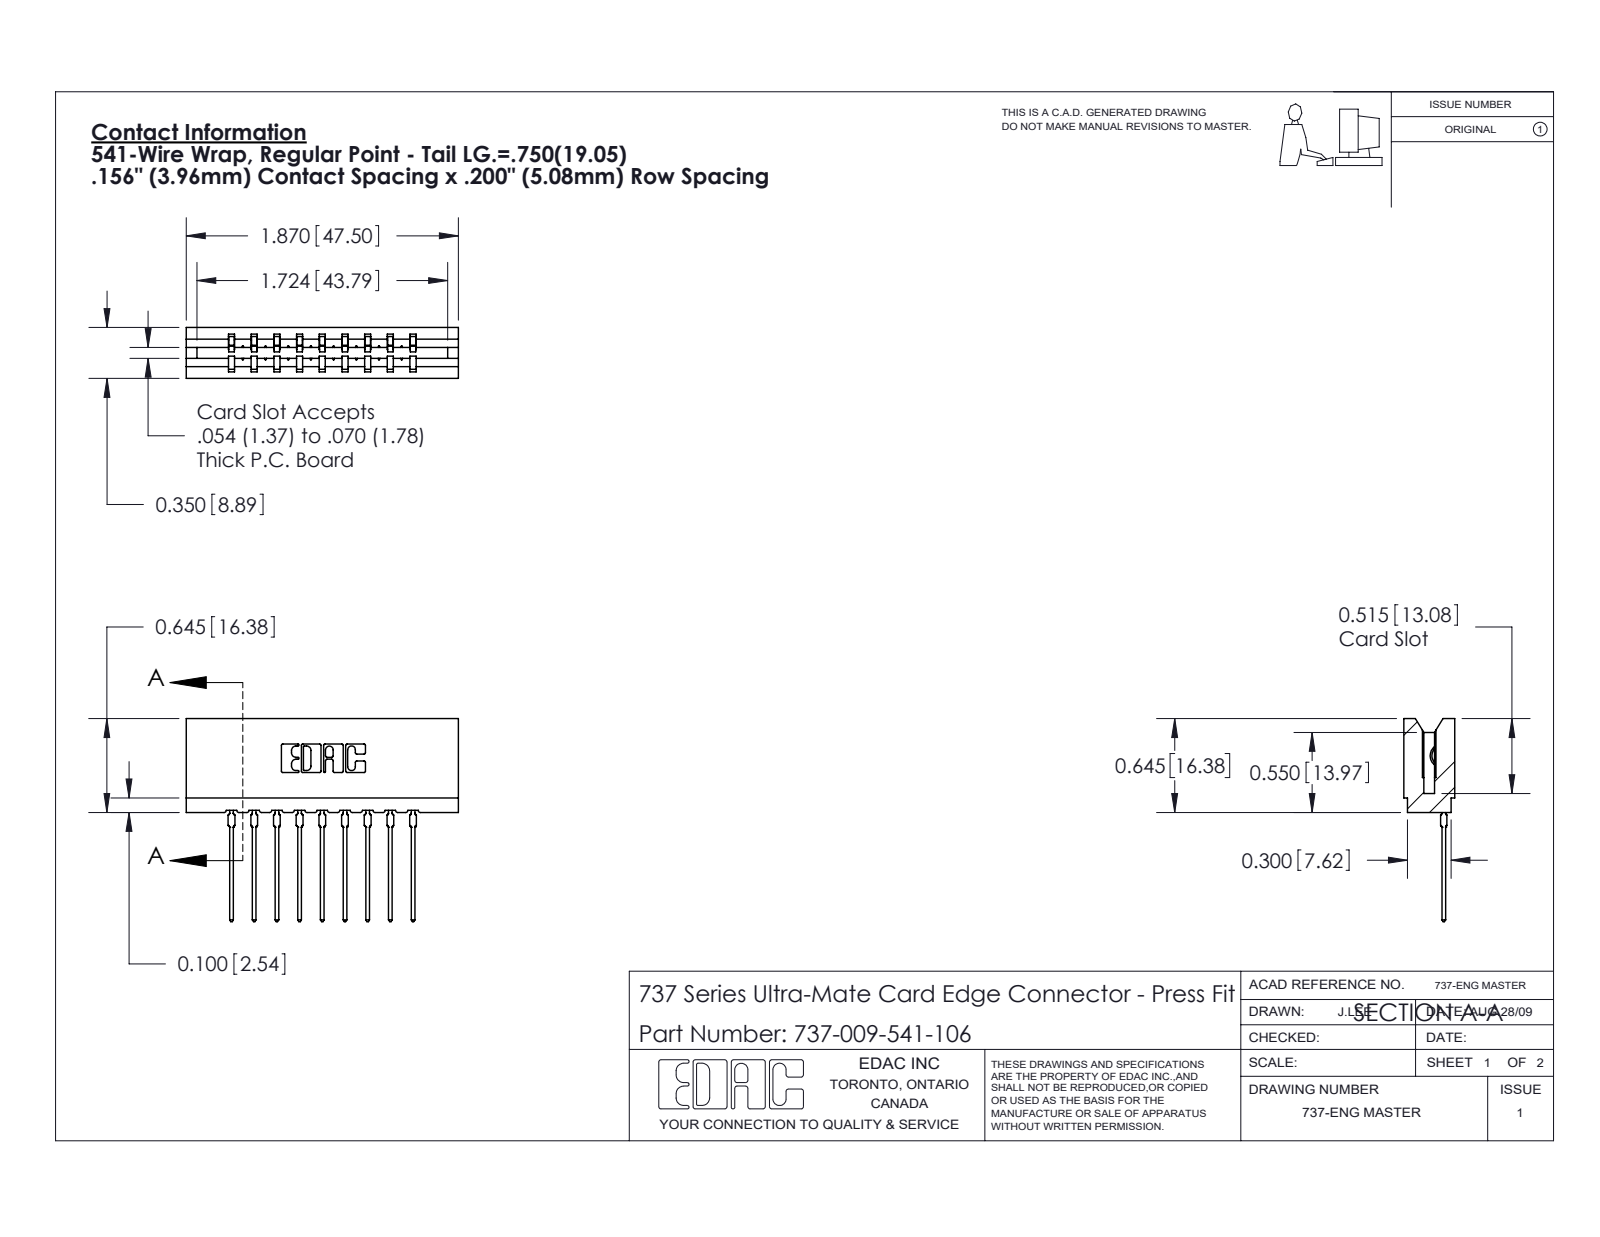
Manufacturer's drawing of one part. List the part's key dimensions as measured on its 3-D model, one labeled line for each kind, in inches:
Part name (STEP PRODUCT): 737-009-541-106; 737 Part_Insulator Option - 06; 745-292-001_541
STEP written by: SolidWorks 2020 (CONFIG_CONTROL_DESIGN)
Units: inches
Bodies: 10 solids, 1112 faces (667 planar, 211 cylindrical, 234 other)
Overall size (bounding box): 1.87 × 1.396 × 0.35
Volume: 0.295 in³ · Surface area: 9.445 in²
Partial cylindrical surfaces — rounded edges, fillets, slot ends (radius × count): R0.01 ×22, R0.015 ×18, R0.021 ×18, R0.007 ×6, R0.031 ×6, R0.005 ×4, R0.011 ×4, R0.026 ×3
Main face-to-face distances: 0.156, 0.138, 0.212, 0.624, 0.35, 0.312, 0.468, 0.354, 0.198, 0.78
